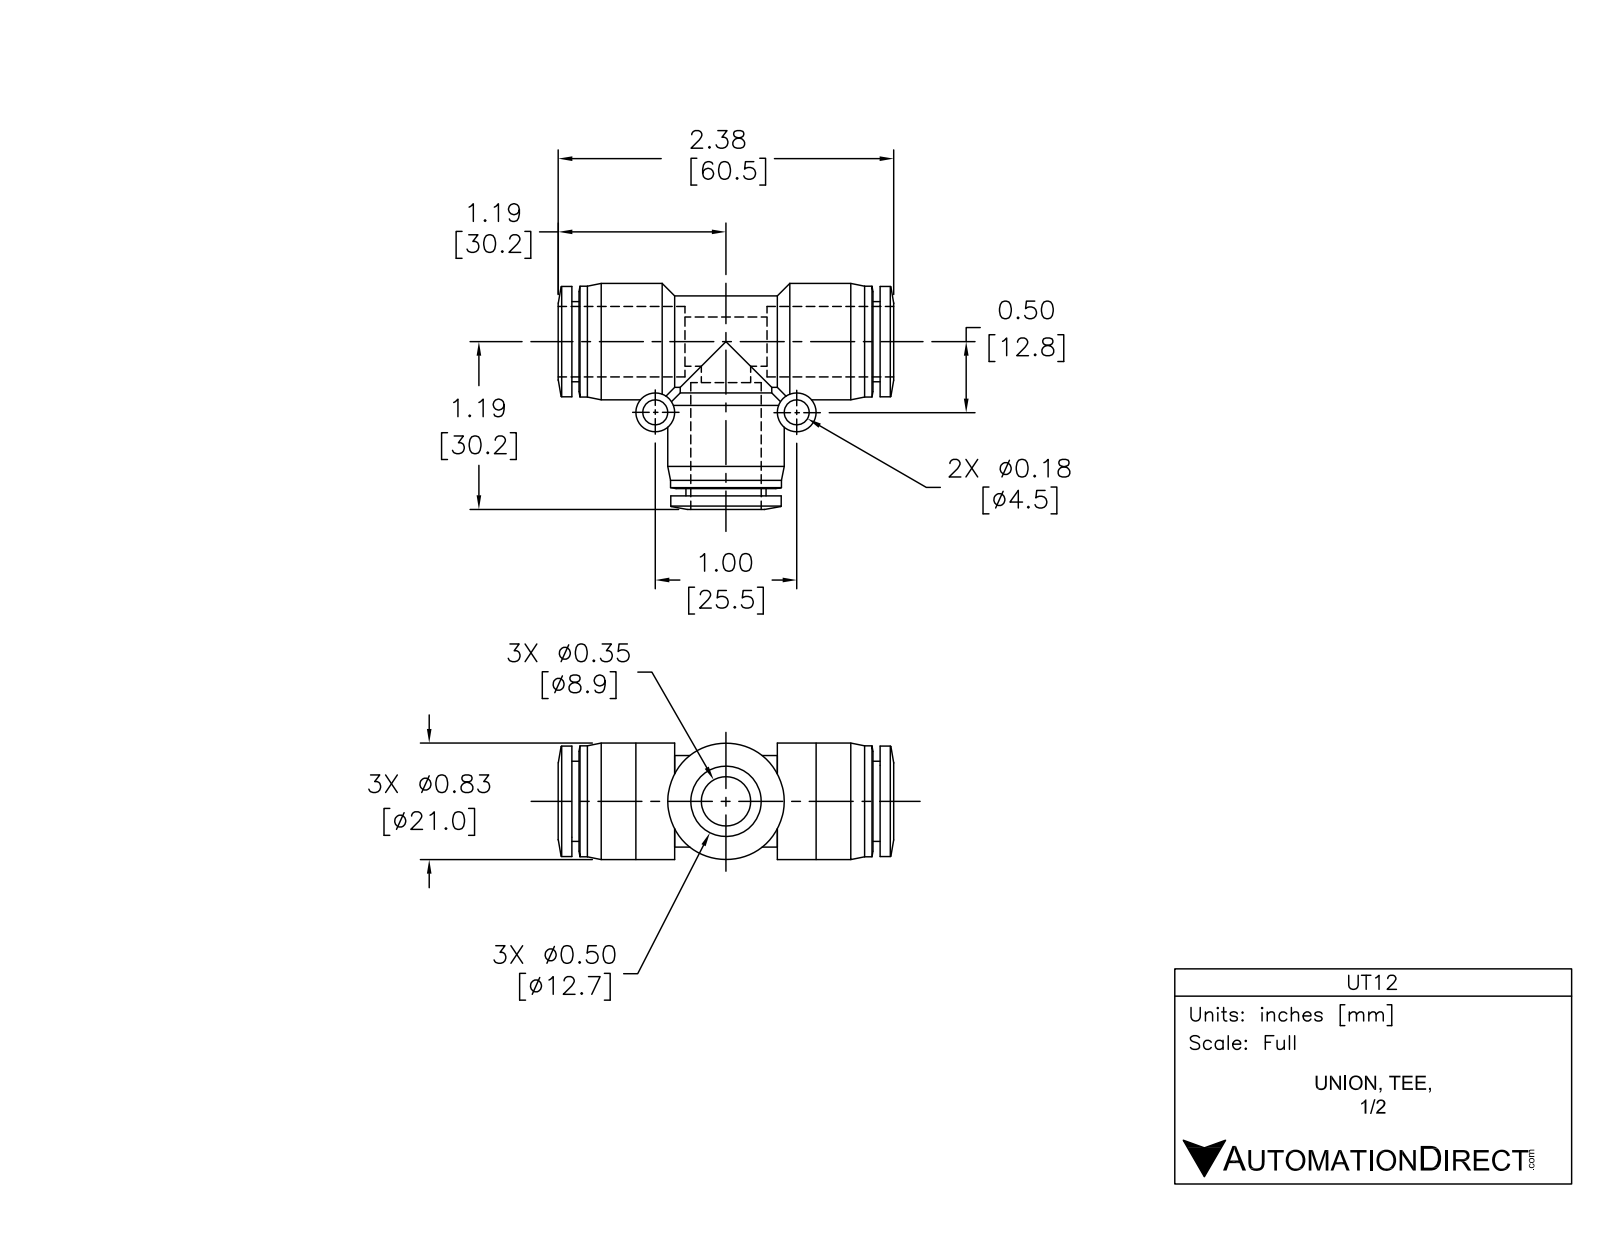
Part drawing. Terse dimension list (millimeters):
name: UT12
written by: SolidWorks 2015 (AUTOMOTIVE_DESIGN)
unit: mm
bodies: 1 solid, 102 faces (13 planar, 47 cylindrical, 42 other)
size: 60.5 × 40.7 × 21
volume: 14 800 mm³; area: 11 050 mm²
holes: 2× ⌀4.5, 2× ⌀10, 2× ⌀13
bosses: 2× ⌀21, 2× ⌀20, 2× ⌀19.9, 2× ⌀16.5, 2× ⌀14.5, 2× ⌀7
face distances: 1.3, 54.3, 20.7, 19.4, 55.6, 35, 33.7, 53, 14.3, 21
hole spacings: 25.5
